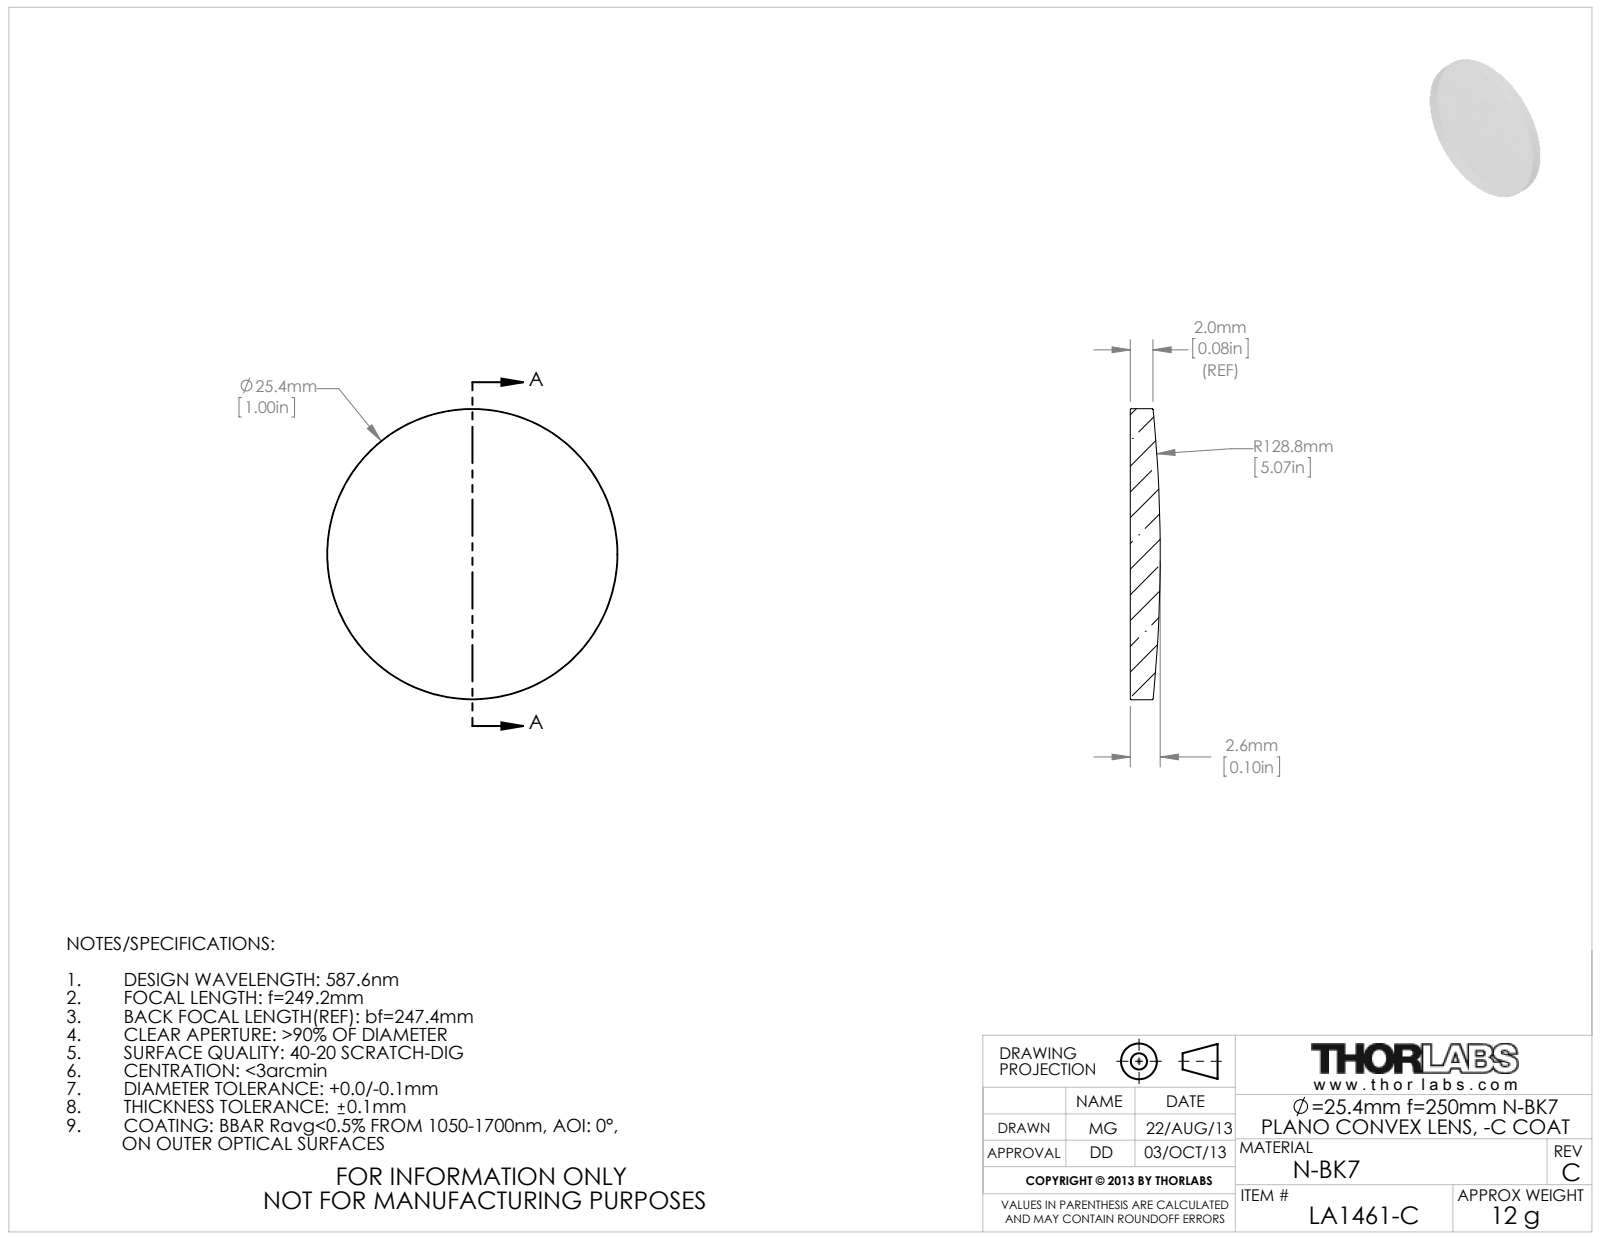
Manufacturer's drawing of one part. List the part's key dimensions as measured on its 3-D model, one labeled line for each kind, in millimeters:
Part name (STEP PRODUCT): 4589-E0W
STEP written by: SolidWorks 2009 (AUTOMOTIVE_DESIGN)
Units: millimetres
Bodies: 1 solid, 5 faces (1 planar, 2 cylindrical, 2 other)
Overall size (bounding box): 25.4 × 25.4 × 2.62
Volume: 1 169 mm³ · Surface area: 1 174 mm²
Round bosses / shafts (diameter × count): ⌀25.4 ×1
